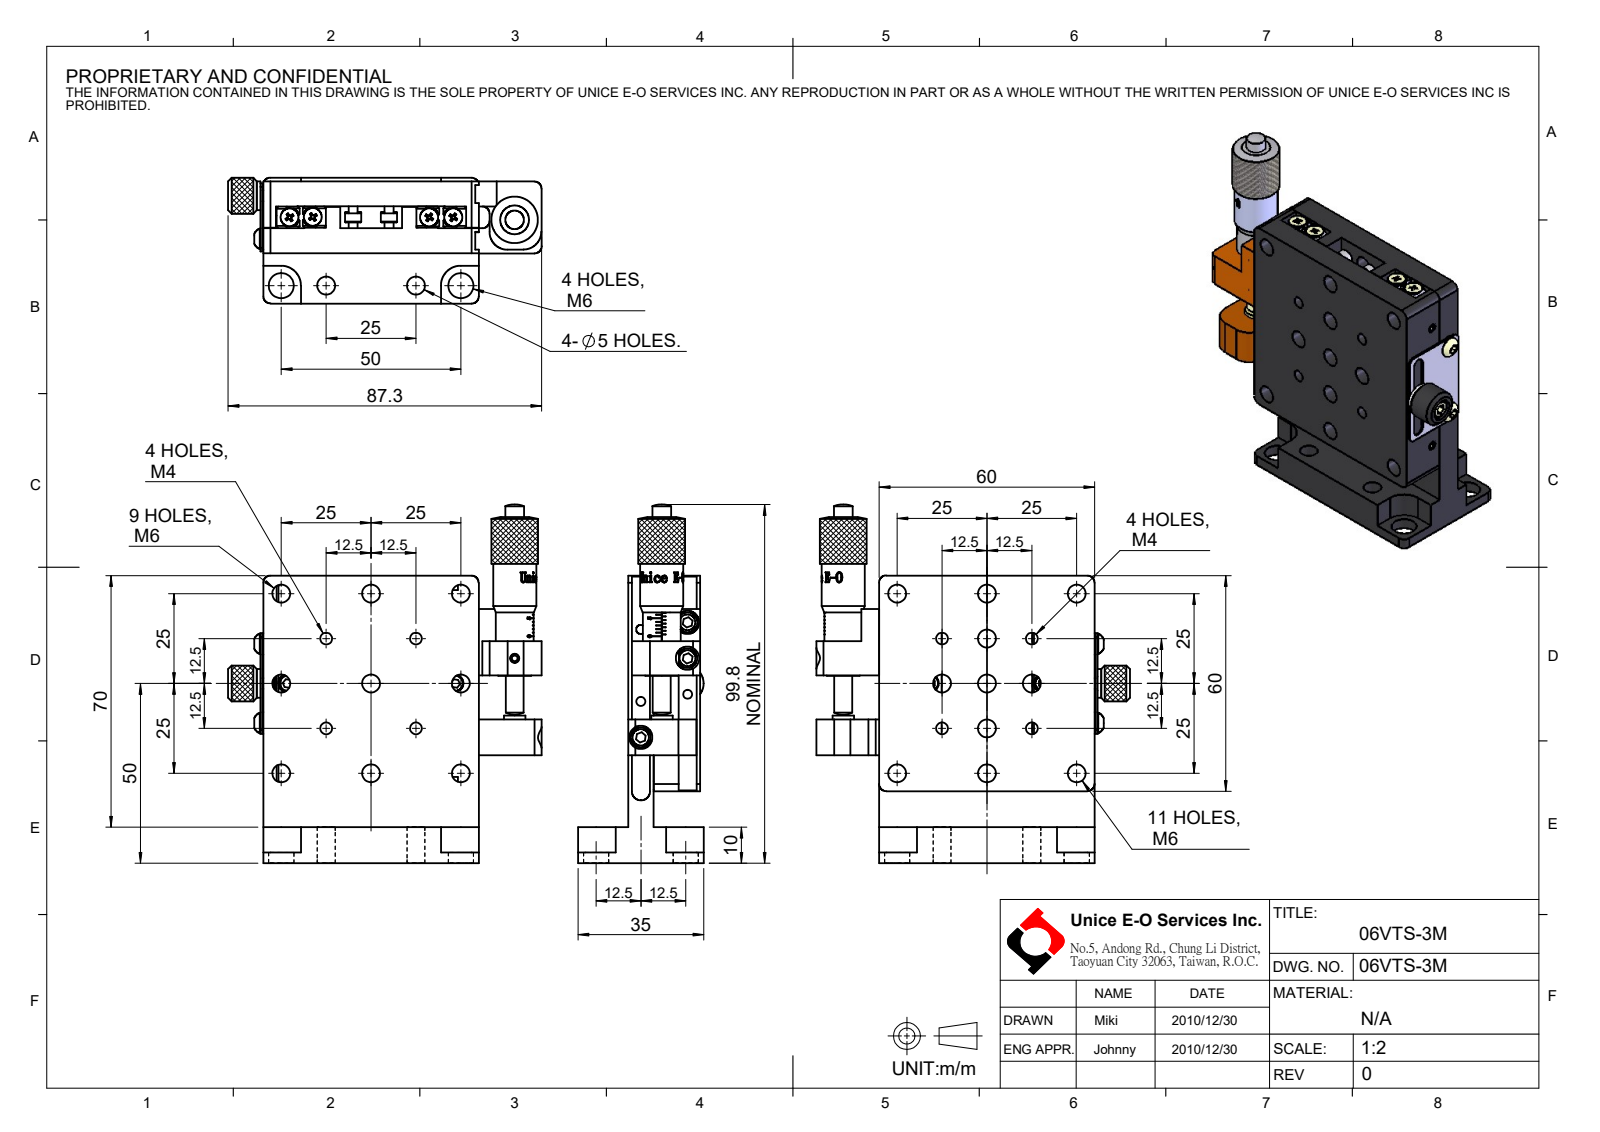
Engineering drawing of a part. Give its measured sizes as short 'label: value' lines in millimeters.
name: 06VTS-3M
written by: SolidWorks 2016 (CONFIG_CONTROL_DESIGN)
unit: mm
bodies: 50 solids, 1652 faces (847 planar, 425 cylindrical, 380 other)
size: 99.79 × 87.3 × 35
volume: 91 645 mm³; area: 51 121 mm²
holes: 30× ⌀5, 20× ⌀2.05, 15× ⌀2.5, 13× ⌀3, 4× ⌀3.3, 4× ⌀7, 3× ⌀3.4, 3× ⌀6.5, 2× ⌀3.2, 2× ⌀3.5, 2× ⌀6, 1× ⌀9.5
bosses: 16× ⌀4.5, 16× ⌀2.5, 9× ⌀3, 4× ⌀5.5, 4× ⌀5, 4× ⌀2.55, 2× ⌀6, 2× ⌀5.7
rounds: 12× R2, 4× R5, 4× R5.5, 2× R1.75, 1× R2.5, 1× R5.98
face distances: 7, 13, 20, 6, 6.9, 6.1, 13.1, 10, 12.9, 5.9
hole spacings: 25, 17.68, 39.53, 20, 35.36, 27.95, 55.9, 10
